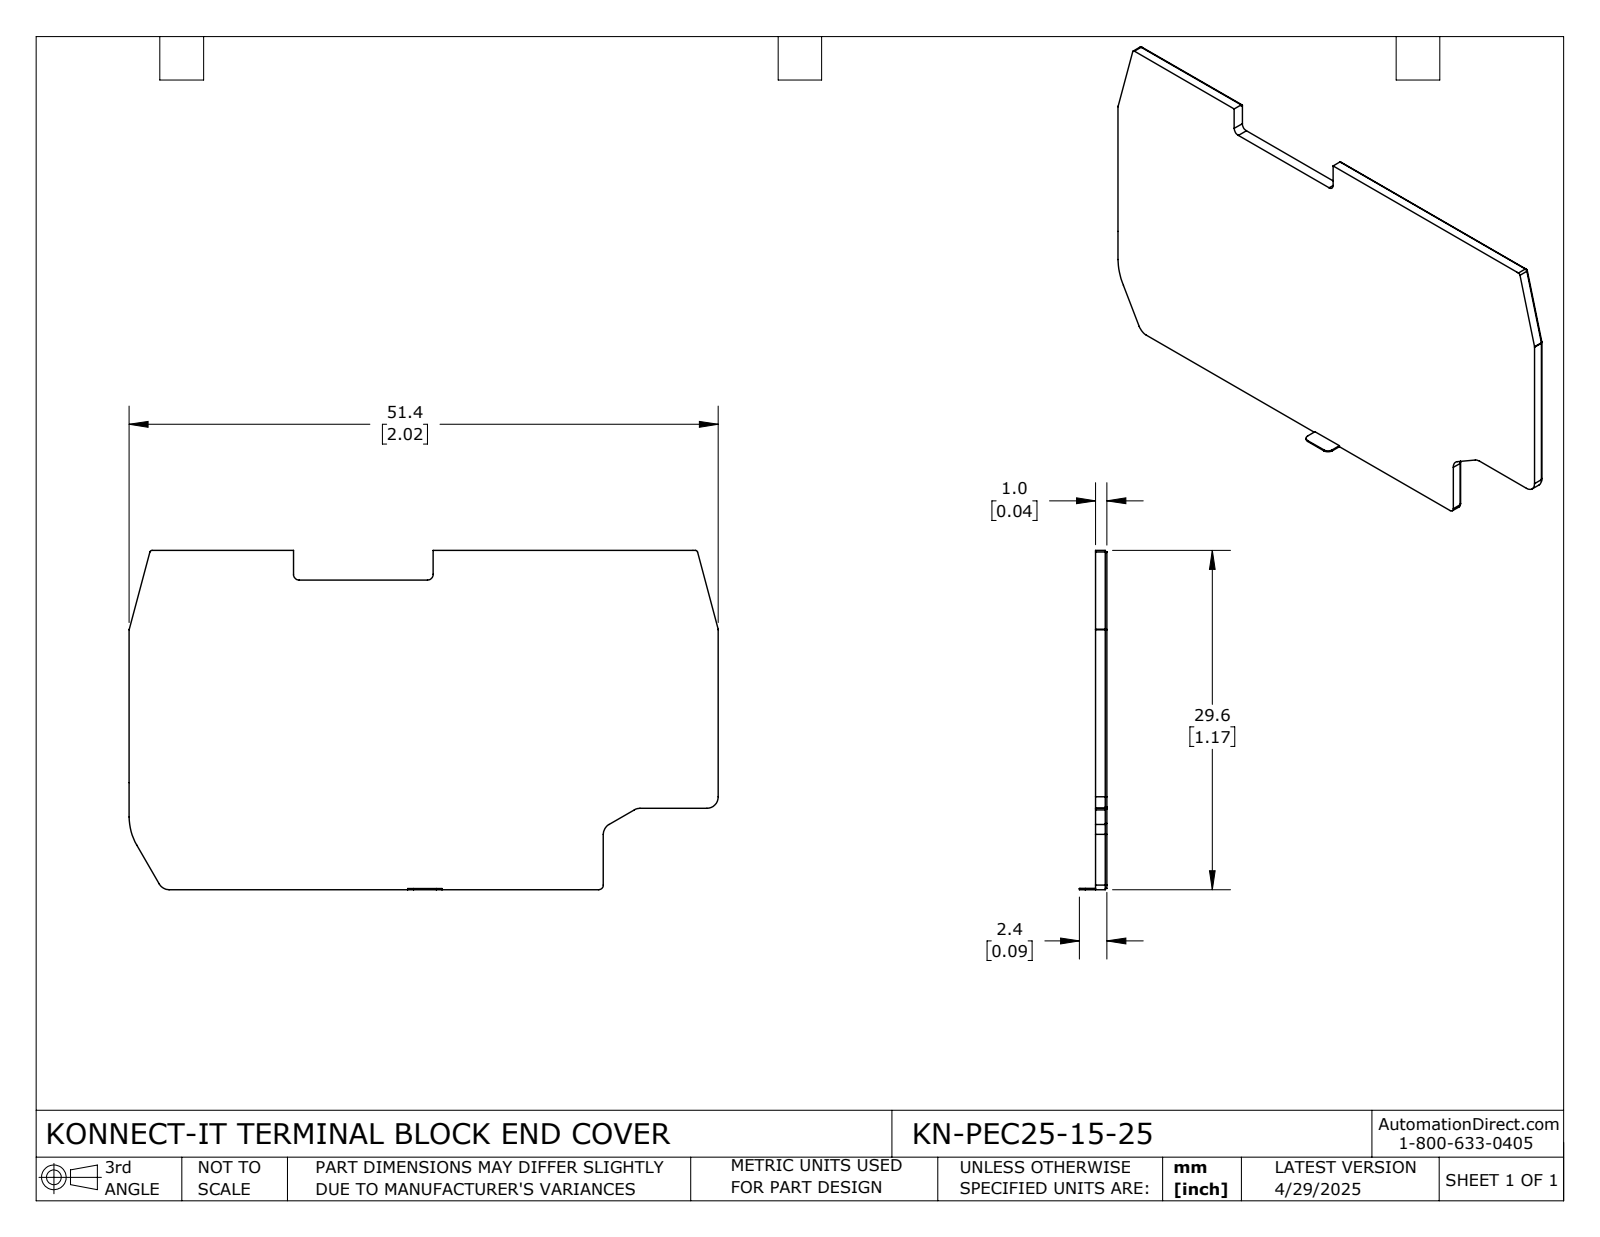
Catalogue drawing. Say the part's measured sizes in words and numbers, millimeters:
The part is named "KN-PEC25-15-25". Its 3-D file was written by "SolidWorks 2024 (CONFIG_CONTROL_DESIGN)". It is 1 solid with 56 faces: 32 planar, 24 cylindrical and 0 other. Overall it measures 51.43 by 29.61 by 2.4 millimeters. Its volume is 1 400 cubic millimeters and its surface area 2 972 square millimeters. Partial cylindrical surfaces (rounded edges, fillets, slot ends): 4 of radius 0.1, 4 of radius 0.2, 4 of radius 0.5, 4 of radius 1, 2 of radius 0.9, 2 of radius 1.1, 1 of radius 0.3, 1 of radius 0.4. The main face-to-face distances are 1, 29.61, 29.51, 0.85, 51.43, 27.02, 2.59, 26.92, 7.1, 22.41.
